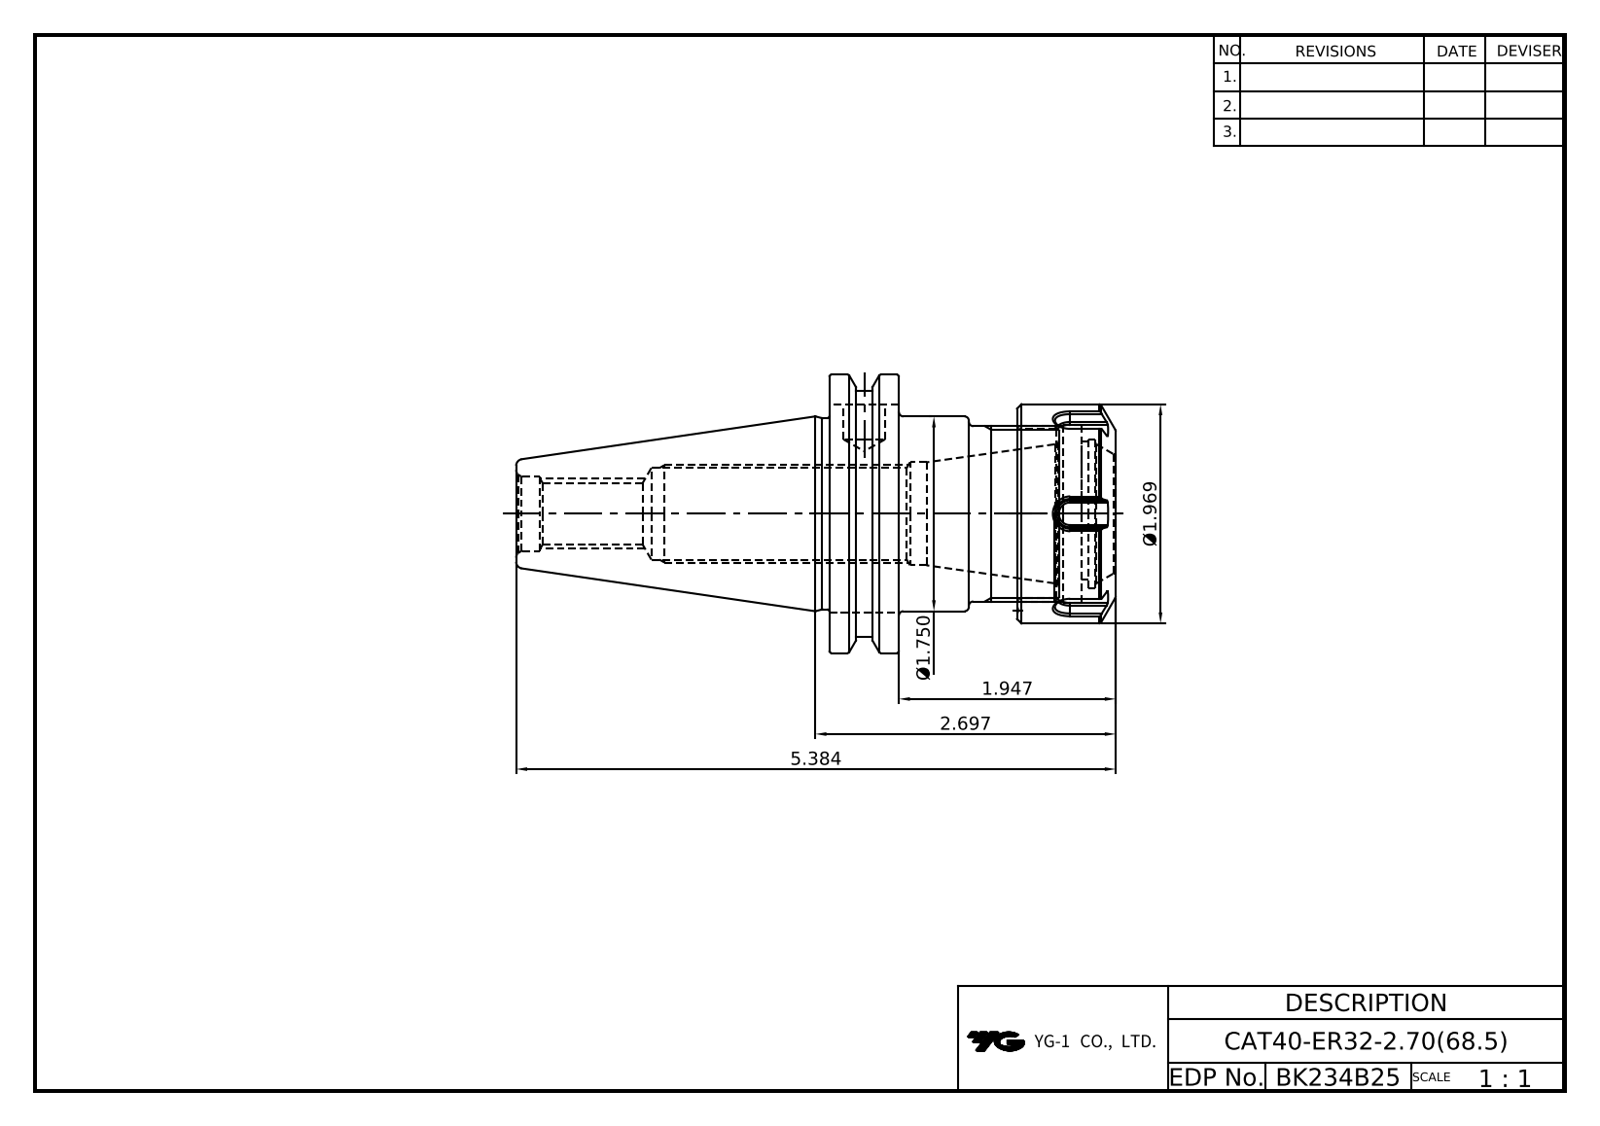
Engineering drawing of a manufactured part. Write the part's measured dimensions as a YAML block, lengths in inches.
part_name: "LO-CAT40-ER32-68.58; ER32NUT"
step_written_by: "Autodesk Inventor 2025 (AUTOMOTIVE_DESIGN)"
units: inches
bodies: {solids: 2, faces: 143, planar: 64, cylindrical: 33, other: 46}
overall_size: [5.387, 2.5, 2.405]
volume: 8.404
surface_area: 58.3
round_holes:
  - {diameter: 0.039, count: 1}
  - {diameter: 0.375, count: 1}
  - {diameter: 0.527, count: 1}
  - {diameter: 0.642, count: 1}
  - {diameter: 0.807, count: 1}
  - {diameter: 0.925, count: 1}
  - {diameter: 1.067, count: 1}
  - {diameter: 1.236, count: 1}
  - {diameter: 1.331, count: 1}
  - {diameter: 1.52, count: 1}
  - {diameter: 1.594, count: 1}
round_bosses_or_shafts:
  - {diameter: 2.5, count: 1}
  - {diameter: 2.217, count: 1}
  - {diameter: 1.969, count: 1}
  - {diameter: 1.75, count: 1}
  - {diameter: 1.717, count: 1}
  - {diameter: 1.575, count: 1}
partial_cylinders:
  - {radius: 0.02, count: 12}
face_to_face_distances: [0.625, 2.575, 1.95, 1.689, 1.064, 0.886, 2.264, 1.639, 0.575, 0.311]
hole_center_spacings: [0.031, 0.866, 0.898]
